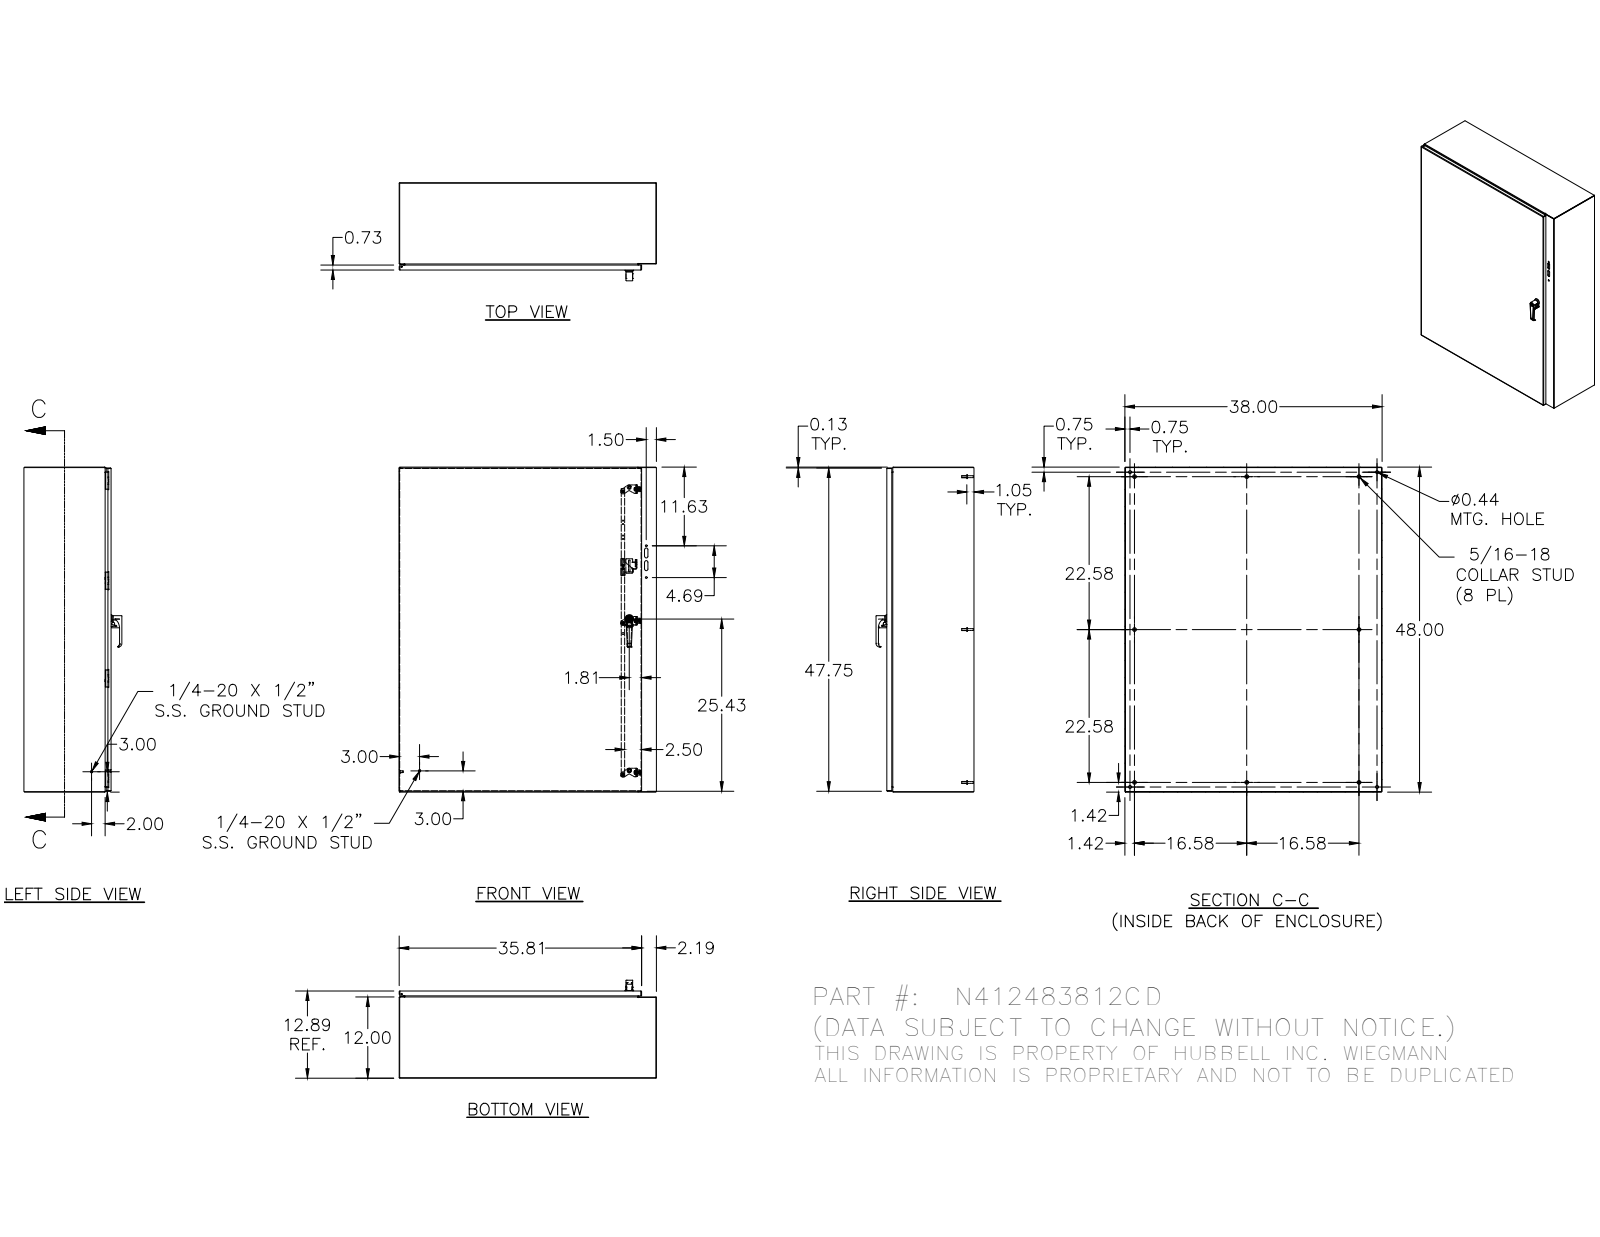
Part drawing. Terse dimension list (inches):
name: N412483812CD
written by: SolidWorks 2019 (AUTOMOTIVE_DESIGN)
unit: in
bodies: 92 solids, 3067 faces (1140 planar, 1136 cylindrical, 791 other)
size: 48 × 38 × 14.512
volume: 456.6 in³; area: 12 274 in²
holes: 9× ⌀0.188, 8× ⌀0.093, 8× ⌀0.152, 8× ⌀0.167, 8× ⌀0.172, 6× ⌀0.145, 6× ⌀0.156, 4× ⌀0.32, 4× ⌀0.438, 3× ⌀0.196, 3× ⌀0.211, 3× ⌀0.22
bosses: 20× ⌀0.25, 14× ⌀0.3, 8× ⌀0.563, 8× ⌀0.36, 8× ⌀0.32, 8× ⌀0.256, 8× ⌀0.164, 8× ⌀0.131
rounds: 50× R0.05, 45× R0.125, 38× R0.02, 34× R0.016, 31× R0.012, 24× R0.025, 22× R0.031, 16× R0.032
face distances: 0.074, 12.843, 12.769, 12.917, 37.926, 47.926, 37.852, 38, 47.852, 48
hole spacings: 14.777, 29.223, 0.5, 19.789, 22.211, 42, 44, 0.66
